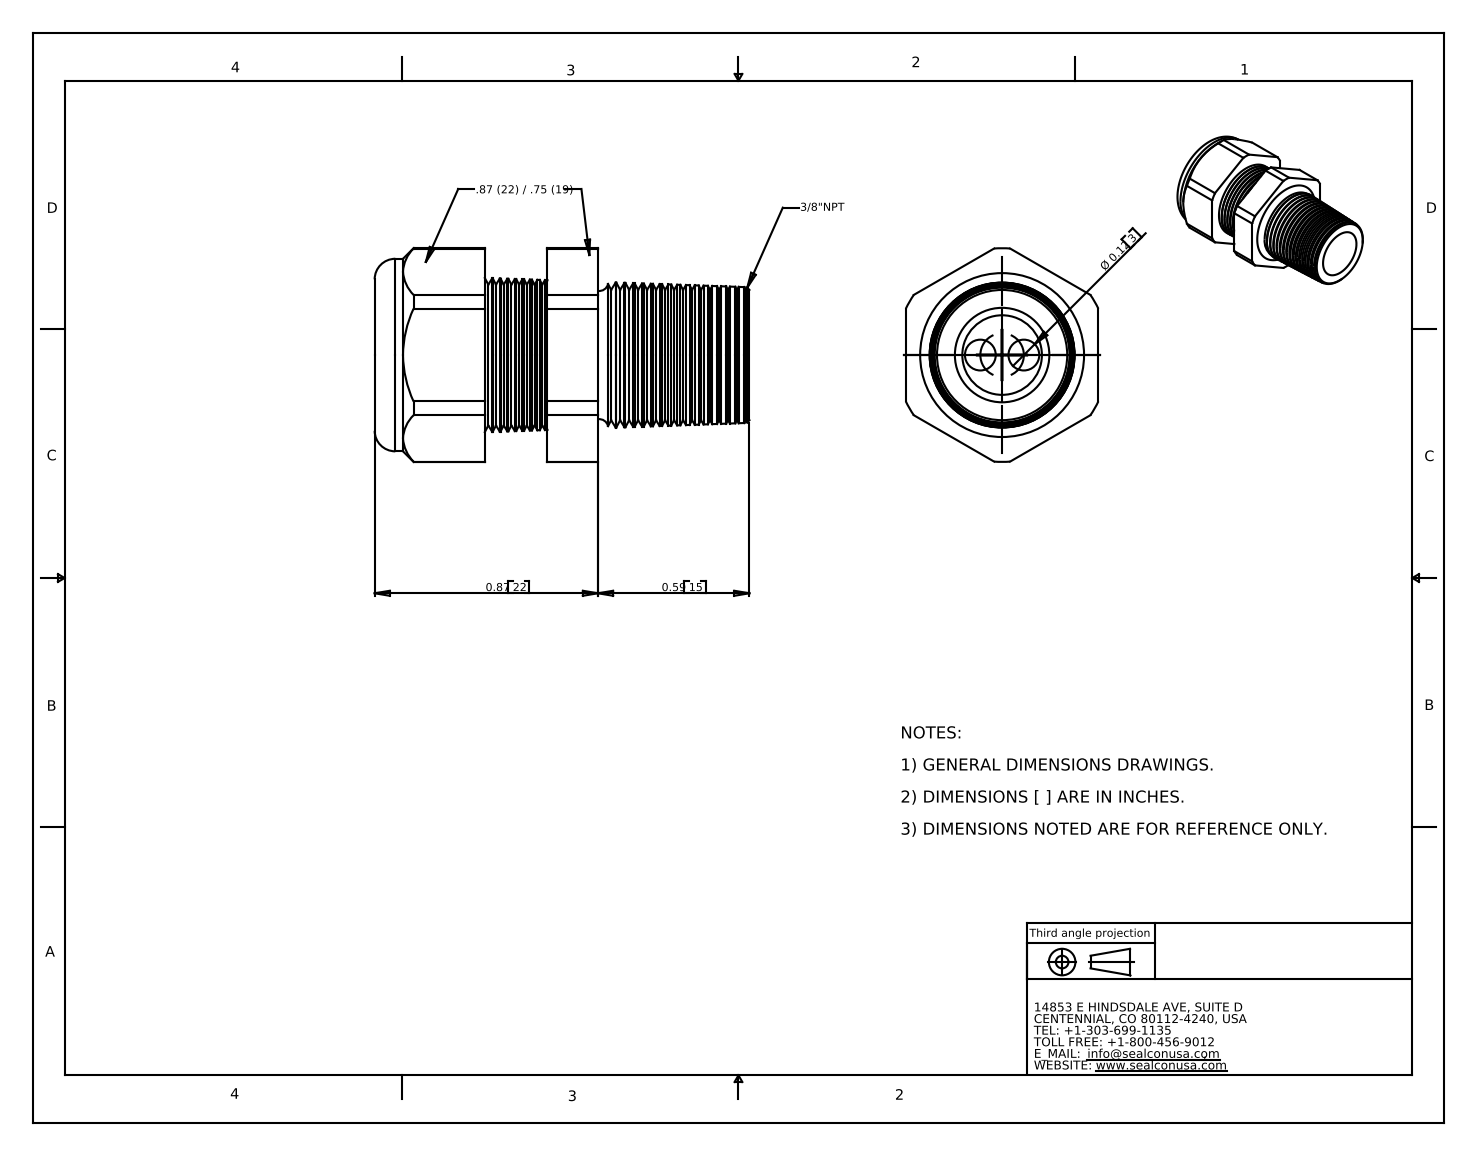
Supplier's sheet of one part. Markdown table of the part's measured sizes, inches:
| quantity | value |
| --- | --- |
| part name | CD09N2-GY |
| STEP written by | SolidWorks 2007 (CONFIG_CONTROL_DESIGN) |
| units | inches |
| bodies | 2 solids, 202 faces (20 planar, 24 cylindrical, 158 other) |
| overall size | 1.46 × 0.833 × 0.75 |
| volume | 0.367 in³ |
| surface area | 7.01 in² |
| round holes (diameter × count) | 0.12 × 2, 0.29 × 1, 0.31 × 1 |
| round bosses / shafts (diameter × count) | 0.75 × 1 |
| partial cylindrical surfaces (radius × count) | 0.416 × 1 |
| main face-to-face distances | 0.75, 0.673, 0.429, 0.244, 0.75, 0.87, 0.441, 0.197, 1.46, 1.031 |
| hole center spacings | 0.085, 0.169 |
